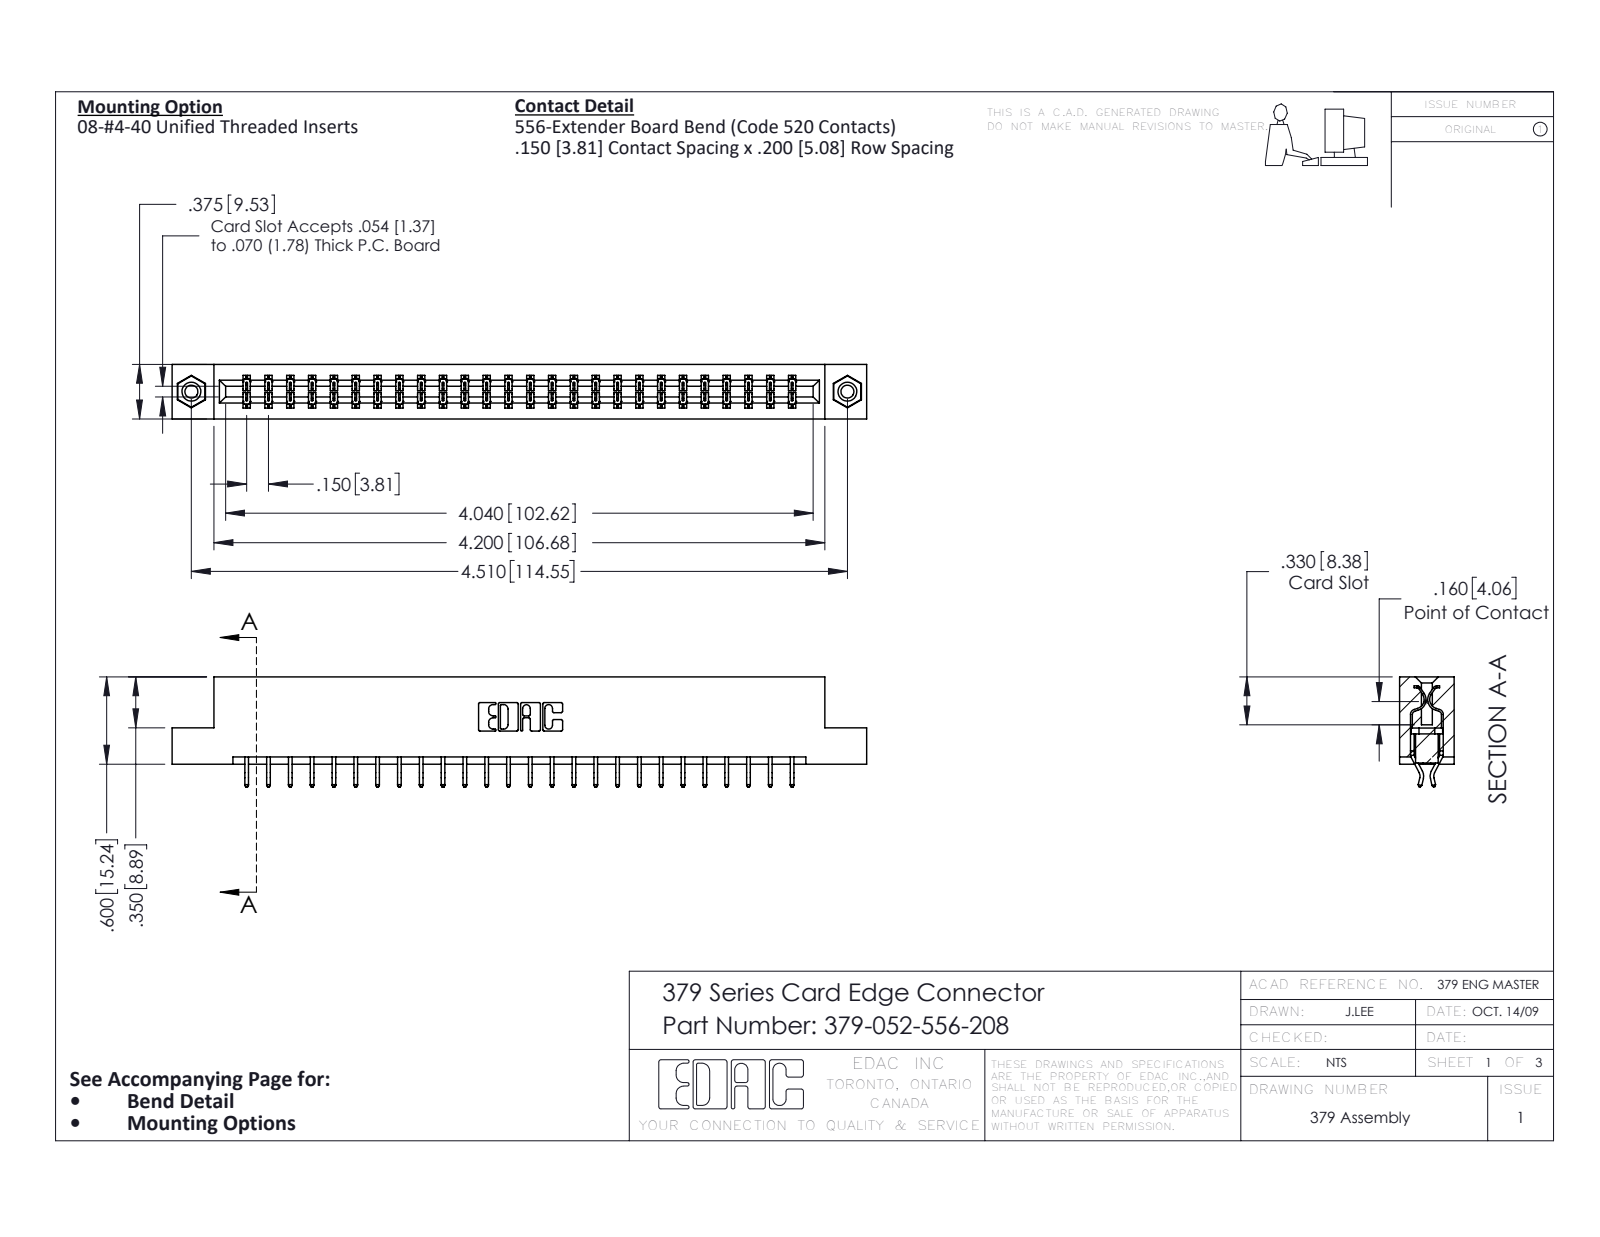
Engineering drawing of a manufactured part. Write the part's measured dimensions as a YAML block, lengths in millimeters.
part_name: "345-292-001_556 Tail; 379 Part_Flush - .156 Dia - TI; 345-250-001_345-250-003-102; 379-052-556-208"
step_written_by: "SolidWorks 2016 (CONFIG_CONTROL_DESIGN)"
units: millimeters
bodies: {solids: 55, faces: 3190, planar: 2182, cylindrical: 992, other: 16}
overall_size: [121.3, 19.2, 9.5]
volume: 12700
surface_area: 14100
round_holes:
  - {diameter: 2.3, count: 2}
  - {diameter: 3.2, count: 2}
  - {diameter: 4, count: 2}
round_bosses_or_shafts:
  - {diameter: 3.9, count: 2}
partial_cylinders:
  - {radius: 0.2, count: 78}
  - {radius: 0.3, count: 22}
  - {radius: 0.2, count: 6}
  - {radius: 0.8, count: 6}
  - {radius: 0.7, count: 3}
  - {radius: 0.3, count: 2}
  - {radius: 0.4, count: 2}
  - {radius: 0.6, count: 2}
face_to_face_distances: [7.6, 1.9, 9.5, 5.1, 5.7, 2.5, 14, 1.9, 3.8, 1.3]
hole_center_spacings: [114.6]
